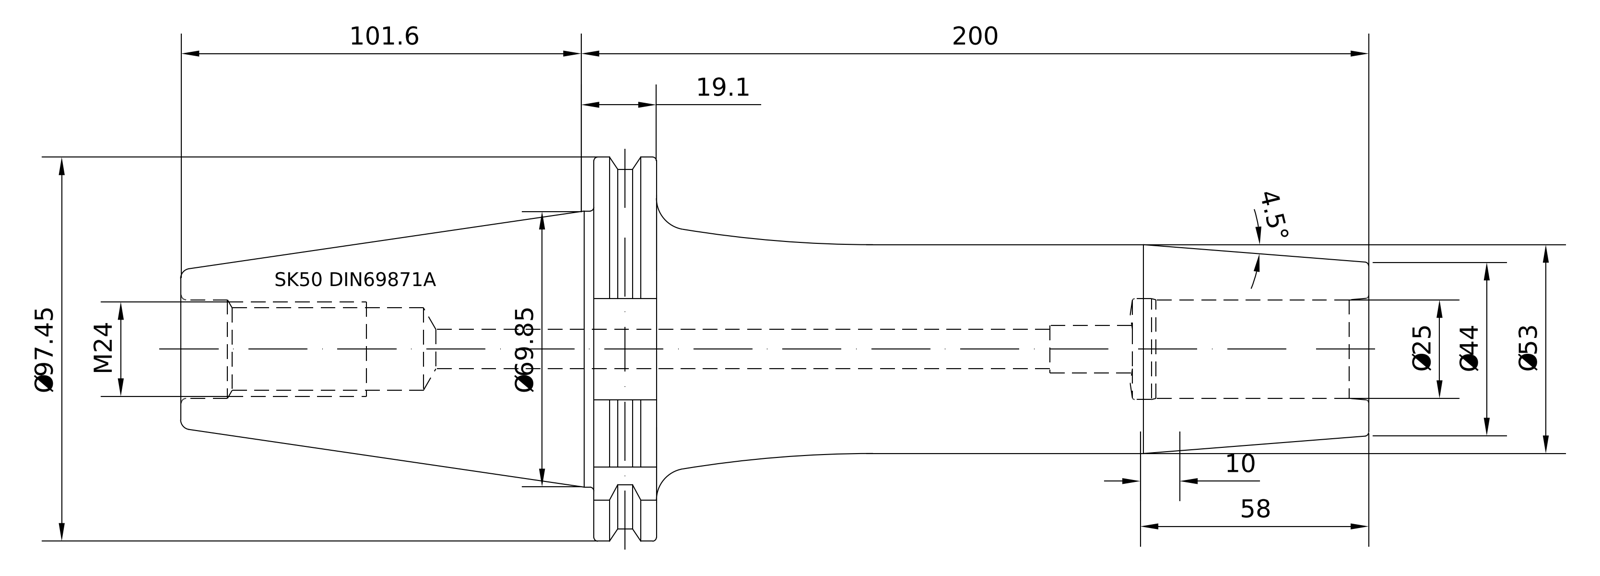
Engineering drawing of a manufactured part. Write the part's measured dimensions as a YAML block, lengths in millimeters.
part_name: "50-446-25"
step_written_by: "PRO/ENGINEER BY PARAMETRIC TECHNOLOGY CORPORATION, 2010430 (CONFIG_CONTROL_DESIGN)"
units: millimeters
bodies: {solids: 1, faces: 96, planar: 22, cylindrical: 24, other: 50}
overall_size: [301.6, 97.47, 94]
volume: 708072
surface_area: 75105
round_holes:
  - {diameter: 20.75, count: 1}
  - {diameter: 25, count: 1}
  - {diameter: 25.01, count: 1}
  - {diameter: 25.7, count: 1}
round_bosses_or_shafts:
  - {diameter: 91, count: 1}
  - {diameter: 69.15, count: 1}
  - {diameter: 53, count: 1}
  - {diameter: 24.01, count: 1}
partial_cylinders:
  - {radius: 1.75, count: 1}
  - {radius: 48.74, count: 1}
face_to_face_distances: [15.85, 196.8, 180.95, 138.8, 122.95, 58, 72.8, 104.8, 120.65, 243.6]
